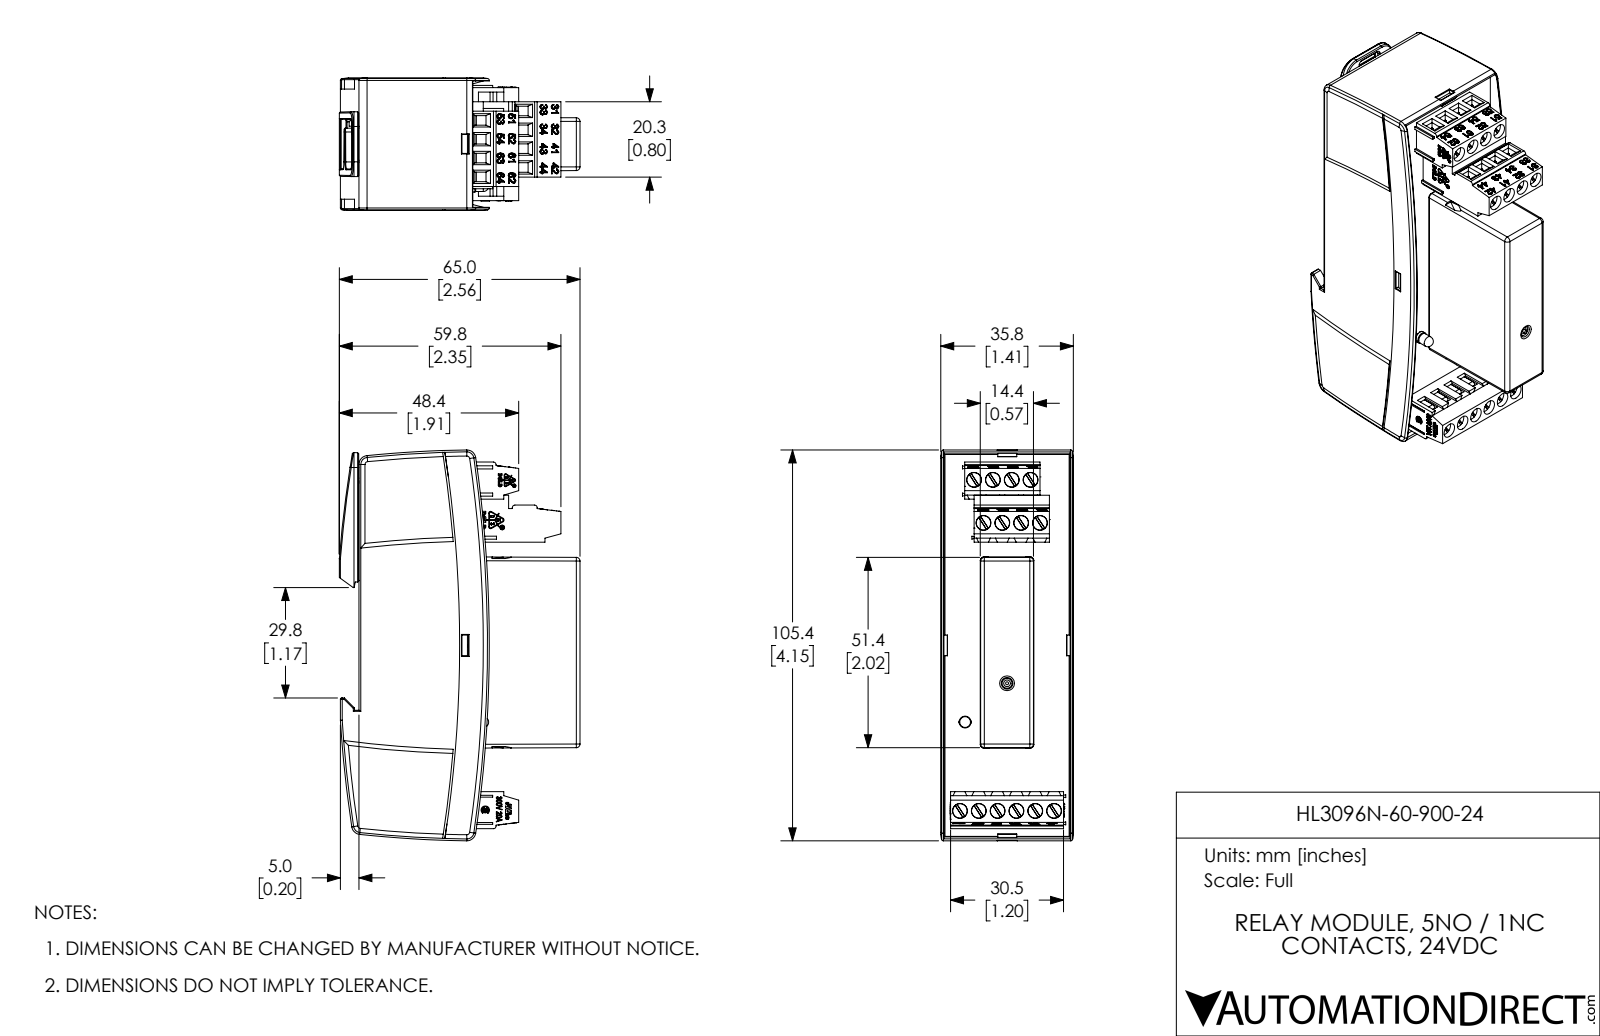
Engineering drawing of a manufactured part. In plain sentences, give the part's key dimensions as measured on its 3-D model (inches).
The part is named "HL3096N-60-900-24". Its 3-D file was written by "SolidWorks 2017 (AUTOMOTIVE_DESIGN)". It is 1 solid with 3802 faces: 2495 planar, 609 cylindrical and 698 other. Overall it measures 4.15 by 2.557 by 1.409 inches. Its volume is 8.974 cubic inches and its surface area 50.77 square inches. Round holes: 27 of diameter 0.059, 14 of diameter 0.157, 2 of diameter 0.022, 2 of diameter 0.035, 1 of diameter 0.019, 1 of diameter 0.034, 1 of diameter 0.037, 1 of diameter 0.05, 1 of diameter 0.06. Round bosses or shafts: 14 of diameter 0.154, 2 of diameter 0.019, 1 of diameter 0.126, 1 of diameter 0.114, 1 of diameter 0.046, 1 of diameter 0.037, 1 of diameter 0.034, 1 of diameter 0.031. Partial cylindrical surfaces (rounded edges, fillets, slot ends): 48 of radius 0.006, 23 of radius 0.02, 21 of radius 0.008, 15 of radius 0.012, 10 of radius 0.039, 7 of radius 0.004, 6 of radius 0.005, 6 of radius 0.005. The main face-to-face distances are 1.402, 1.154, 0.026, 1.409, 1.394, 1.376, 0.033, 1.368, 1.195, 1.343. The hole center spacings are 0.394, 0.2, 0.197, 0.44, 0.4, 0.557, 0.467, 0.591.
